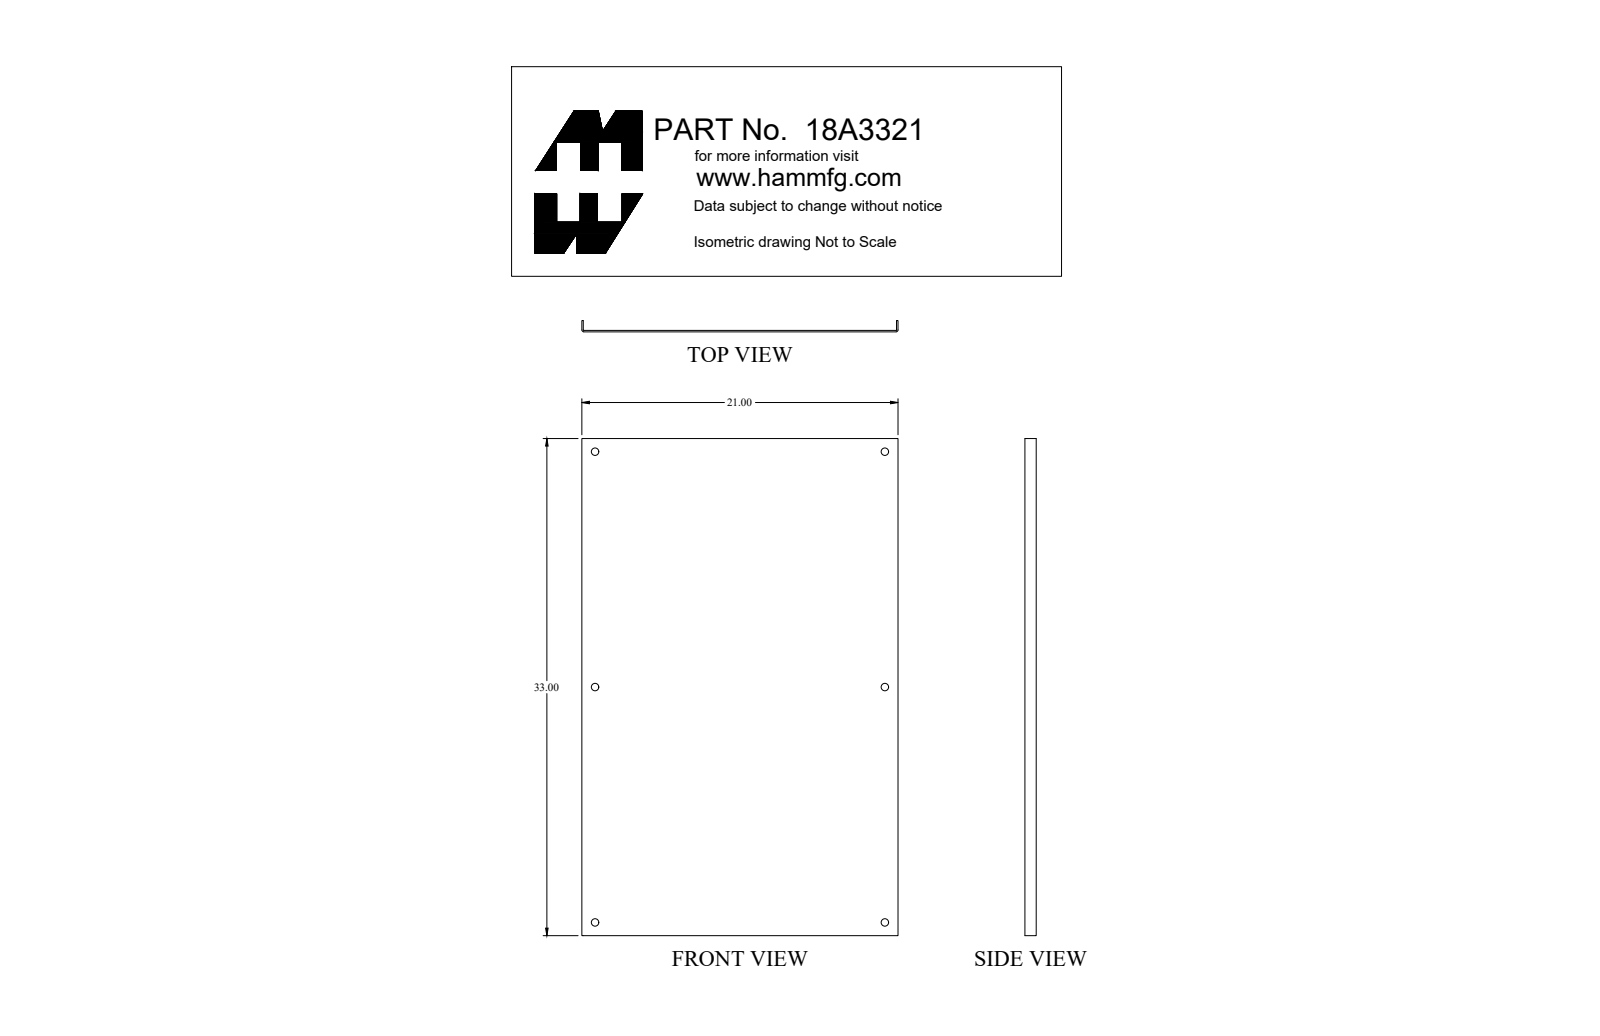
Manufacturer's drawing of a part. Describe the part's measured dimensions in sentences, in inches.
The part is named "18A3321". Its 3-D file was written by "SolidWorks 2018 (AUTOMOTIVE_DESIGN)". It is 1 solid with 20 faces: 10 planar, 10 cylindrical and 0 other. Overall it measures 33 by 21 by 0.75 inches. Its volume is 69.62 cubic inches and its surface area 1 477 square inches. Round holes: 6 of diameter 0.5. Partial cylindrical surfaces (rounded edges, fillets, slot ends): 2 of radius 0.03, 2 of radius 0.125. The main face-to-face distances are 0.095, 20.905, 21, 20.81, 0.75, 0.655, 33. The hole center spacings are 15.625, 24.793, 19.25, 31.25, 36.703.
